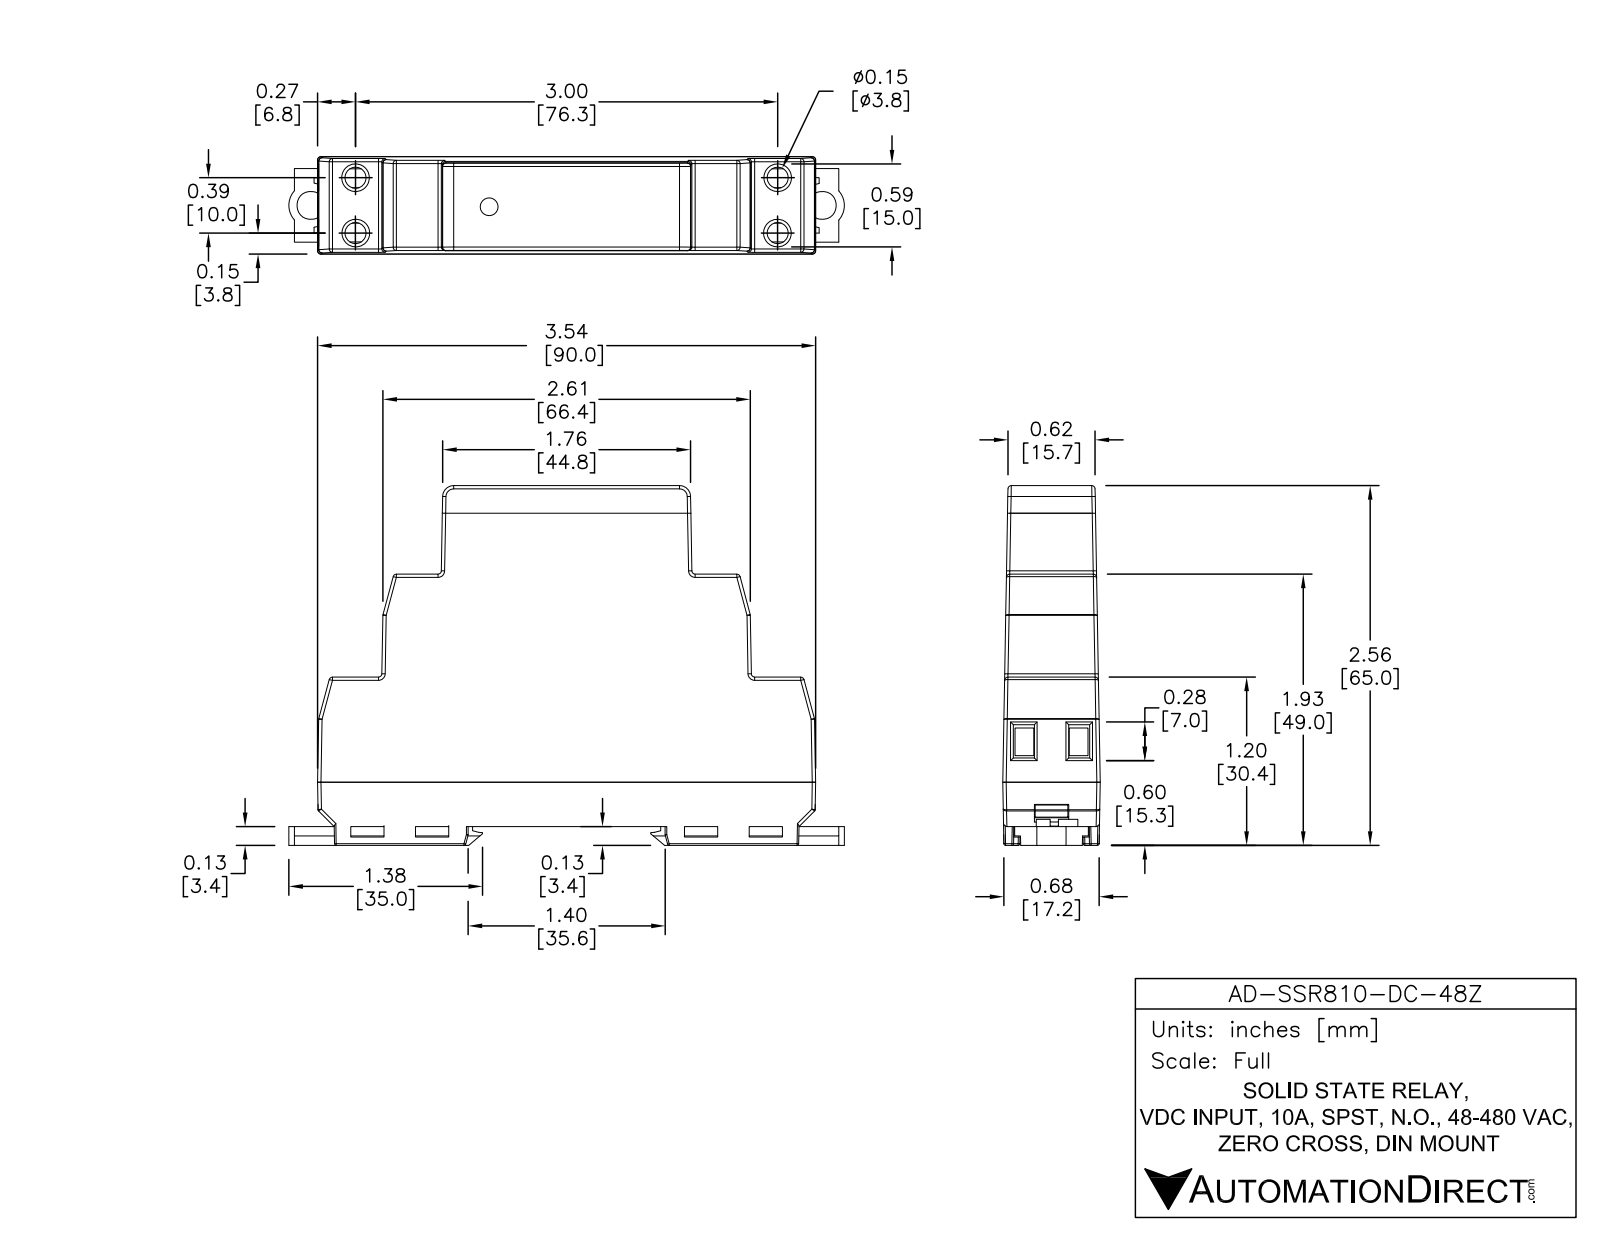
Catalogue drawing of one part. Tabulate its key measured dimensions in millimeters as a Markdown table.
| quantity | value |
| --- | --- |
| part name | AD-SSR810-DC-48Z |
| STEP written by | SolidWorks 2013 (AUTOMOTIVE_DESIGN) |
| units | millimeters |
| bodies | 1 solid, 838 faces (500 planar, 78 cylindrical, 260 other) |
| overall size | 99.7 × 66.4 × 17.4 |
| volume | 75 460 mm³ |
| surface area | 15 630 mm² |
| round holes (diameter × count) | 4.8 × 4, 5.1 × 2 |
| round bosses / shafts (diameter × count) | 2.7 × 1 |
| partial cylindrical surfaces (radius × count) | 0.4 × 41, 1.5 × 2, 4.4 × 2 |
| main face-to-face distances | 64.1, 1.2, 65.4, 10.8, 56.3, 0.6, 1.3, 49.1, 47.9, 16.3 |
| hole center spacings | 8.6, 83.8, 9.2, 76.5, 77, 90.9 |
